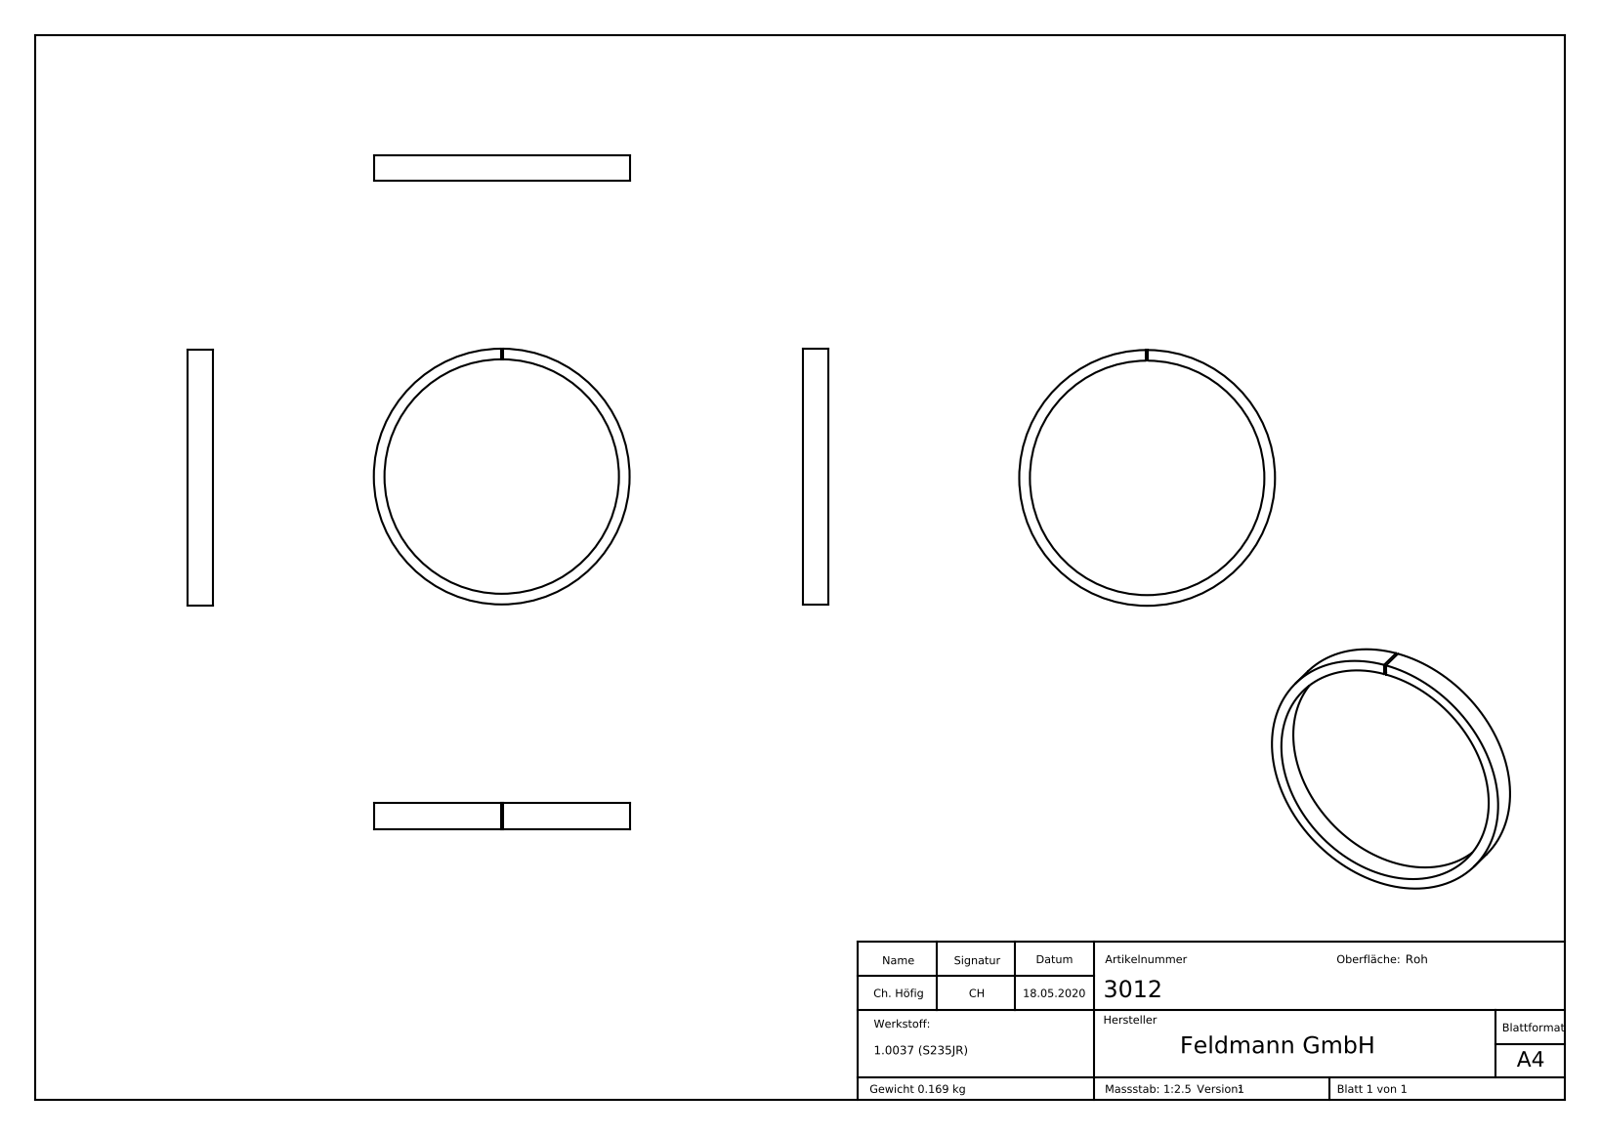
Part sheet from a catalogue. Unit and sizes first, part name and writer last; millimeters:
Units: millimetres
Overall size (bounding box): 120 × 120 × 12
Round holes (diameter × count): ⌀110 ×1
Round bosses / shafts (diameter × count): ⌀120 ×1
Main face-to-face distances: 12, 1, 1.1, 1.78, 1.21, 0.83, 0.99, 2.77, 1.71, 2.45
Volume: 21 617 mm³ · Surface area: 12 374 mm²
Bodies: 1 solid, 168 faces (89 planar, 2 cylindrical, 77 other)
Part name (STEP PRODUCT): 3012
STEP written by: SolidWorks 2015 (CONFIG_CONTROL_DESIGN)
